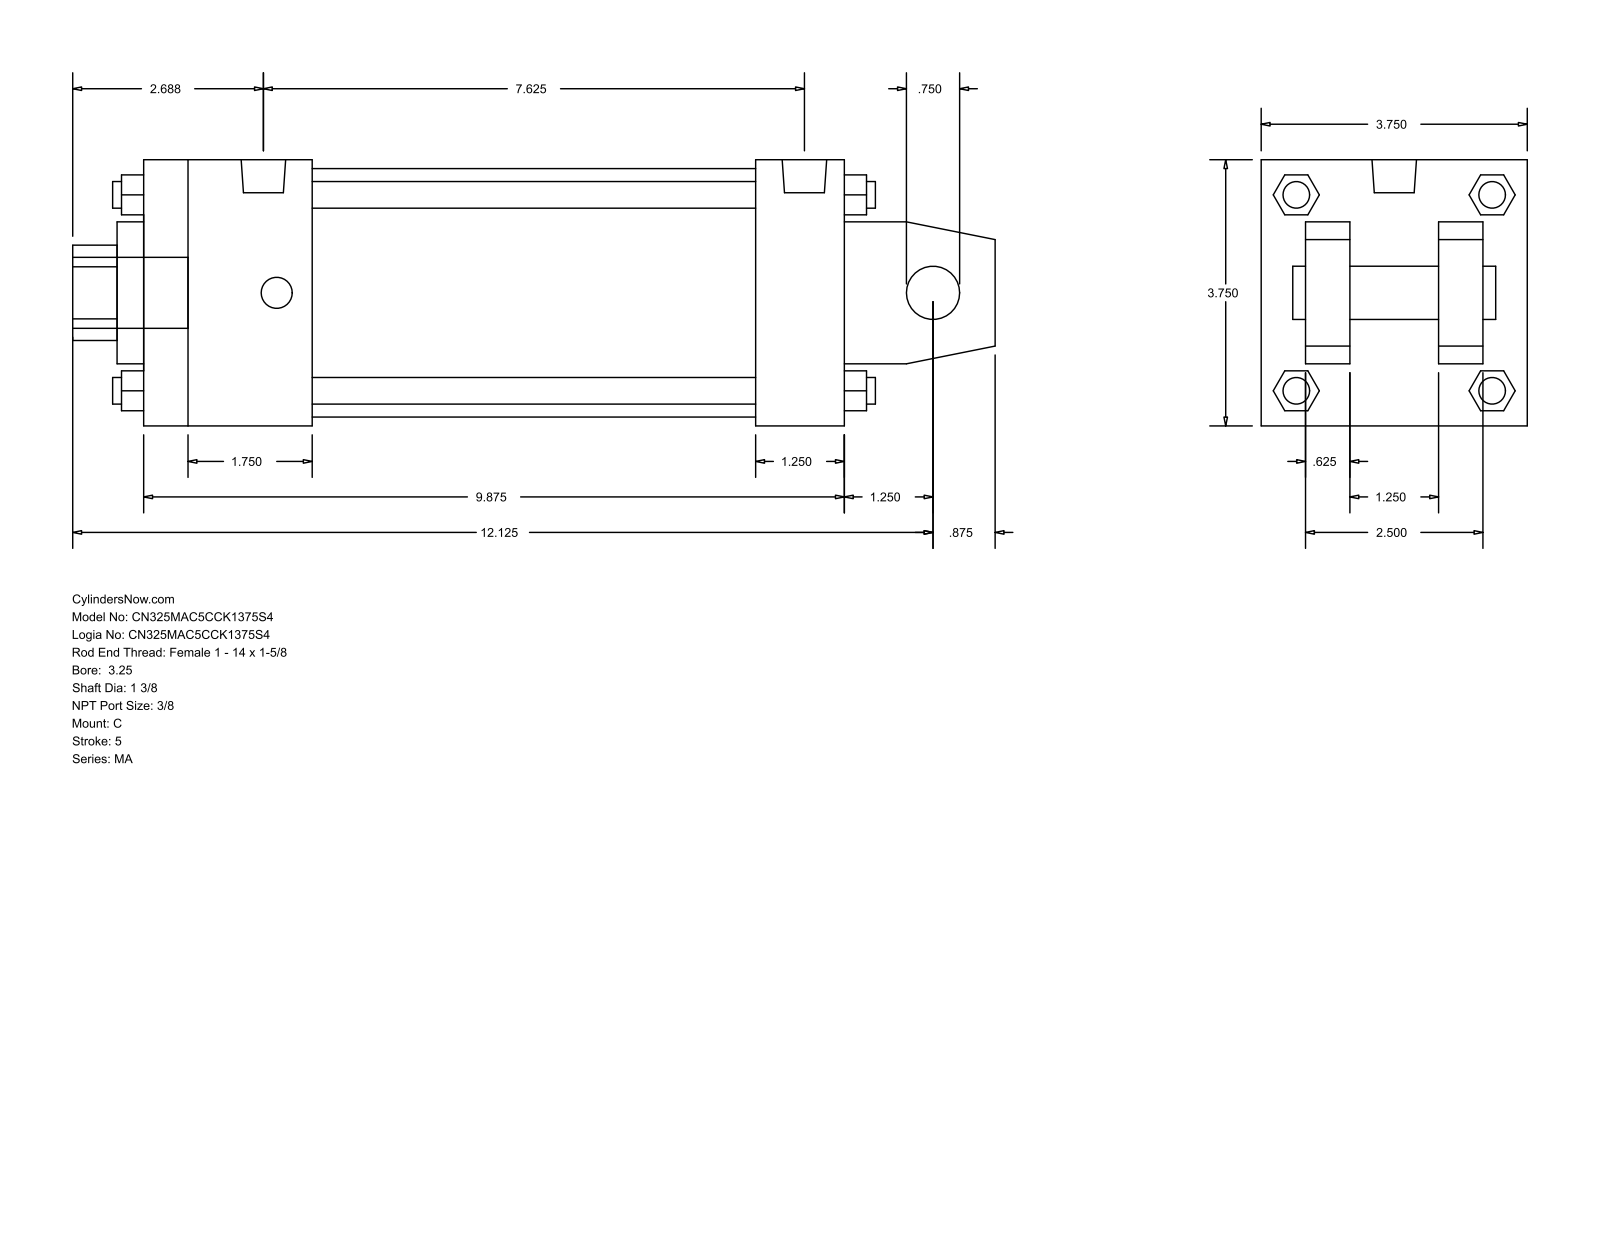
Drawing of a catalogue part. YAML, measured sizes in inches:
part_name: "MA_C__0325_1.375"
step_written_by: "GSSL Pune (CONFIG_CONTROL_DESIGN)"
units: inches
bodies: {solids: 0, faces: 139, planar: 108, cylindrical: 31, other: 0}
overall_size: [13, 3.75, 3.75]
round_holes:
  - {diameter: 0.75, count: 1}
  - {diameter: 1.375, count: 1}
  - {diameter: 2, count: 1}
  - {diameter: 3.5, count: 1}
round_bosses_or_shafts:
  - {diameter: 0.437, count: 4}
  - {diameter: 0.375, count: 4}
  - {diameter: 0.627, count: 2}
  - {diameter: 1, count: 1}
partial_cylinders:
  - {radius: 0.672, count: 1}
face_to_face_distances: [3.75, 0.625, 2.5, 9.875, 1.25, 1.25, 3.125, 1.875, 8.625, 2.375]
